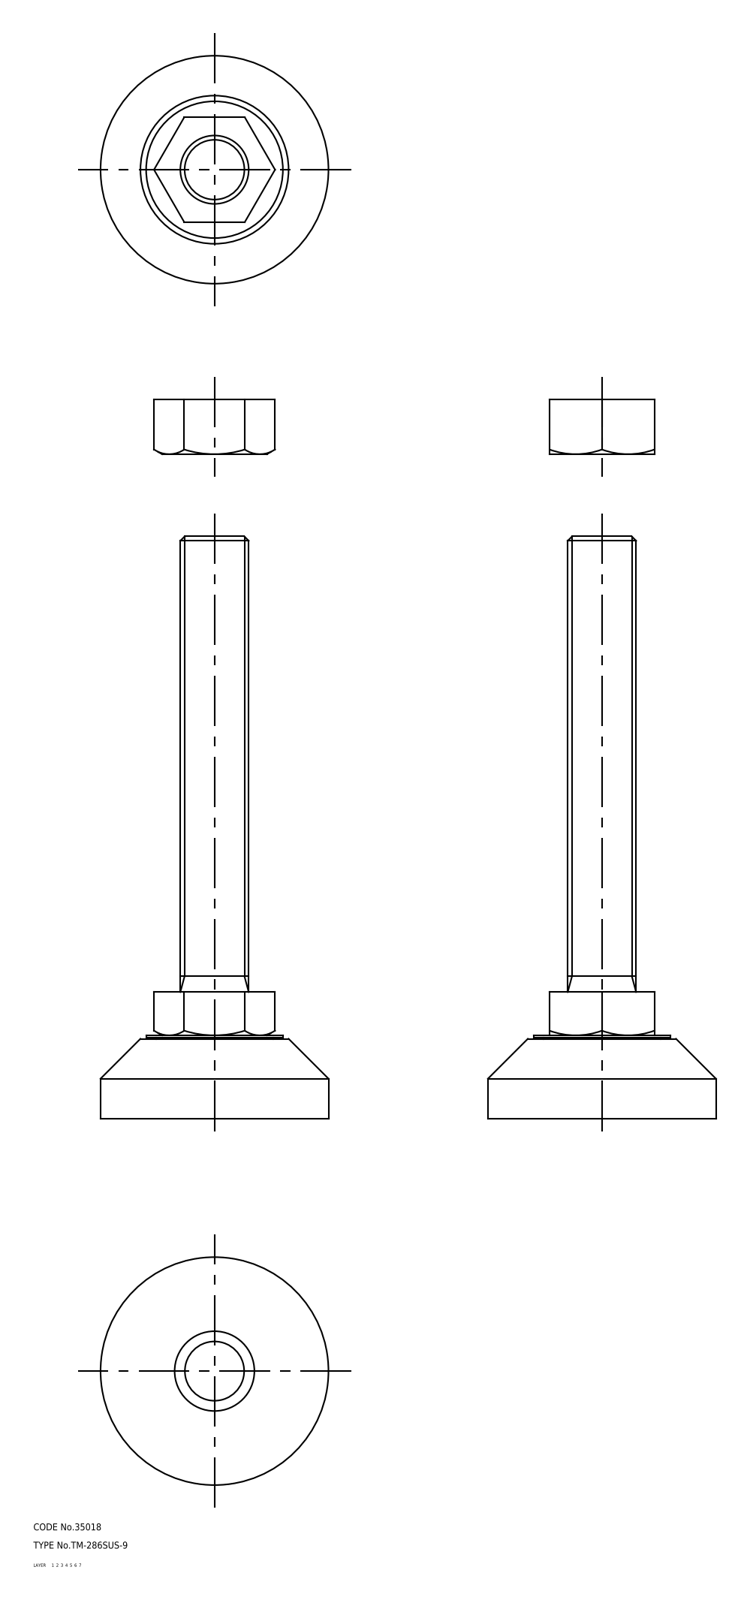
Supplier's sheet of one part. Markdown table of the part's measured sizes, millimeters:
| quantity | value |
| --- | --- |
| part name | 67111650; 67111663 |
| STEP written by | CADfix (AUTOMOTIVE_DESIGN) |
| units | millimeters |
| bodies | 2 solids, 52 faces (0 planar, 0 cylindrical, 52 other) |
| overall size | 255.5 × 100 × 100 |
| volume | 434 127 mm³ |
| surface area | 56 366 mm² |
